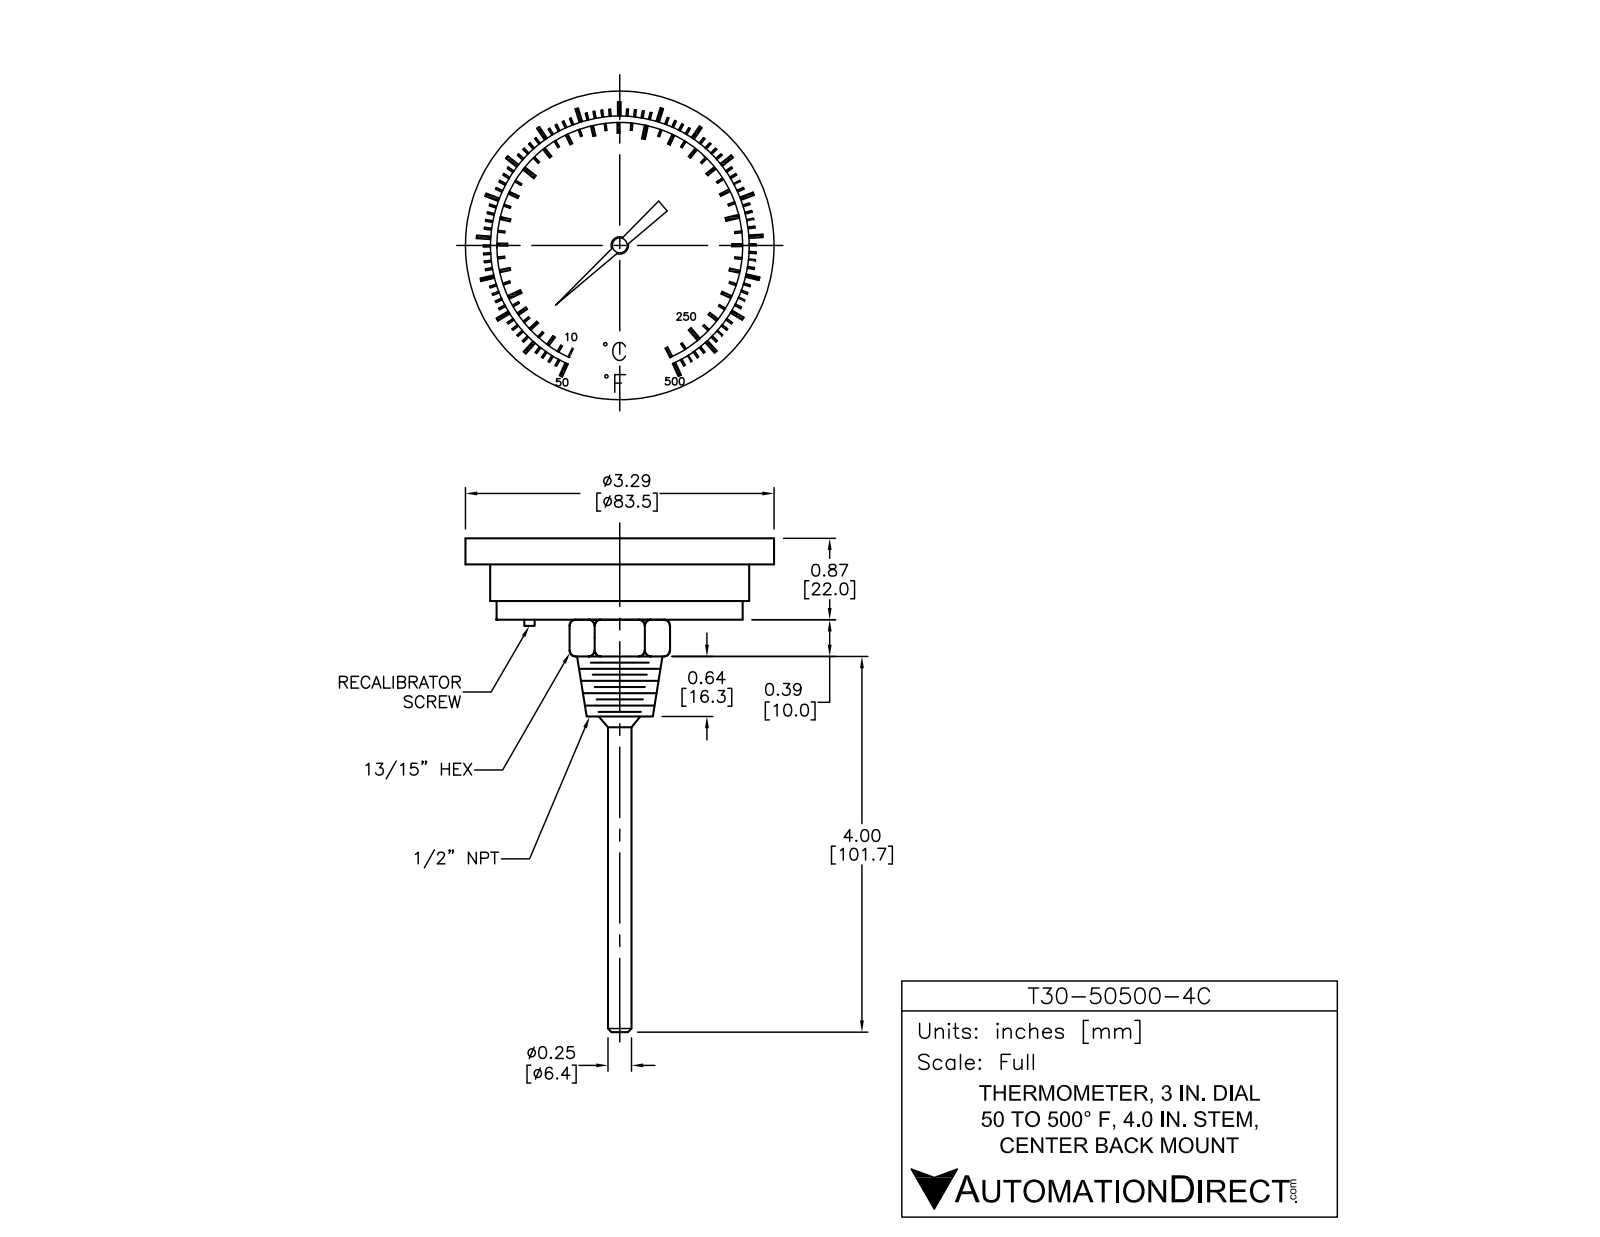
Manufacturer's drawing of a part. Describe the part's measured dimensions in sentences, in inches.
The part is named "T30-50500-4C". Its 3-D file was written by "SolidWorks 2021 (AUTOMOTIVE_DESIGN)". It is 57 solids with 934 faces: 720 planar, 124 cylindrical and 90 other. Overall it measures 5.26 by 3.29 by 3.29 inches. Its volume is 3.15 cubic inches and its surface area 34.08 square inches. Round holes: 1 of diameter 0.067, 1 of diameter 2.69. Round bosses or shafts: 1 of diameter 3.29, 1 of diameter 2.76, 1 of diameter 2.62, 1 of diameter 0.846, 1 of diameter 0.258. Partial cylindrical surfaces (rounded edges, fillets, slot ends): 1 of radius 0.04, 1 of radius 0.859, 1 of radius 0.969. The main face-to-face distances are 0.222, 0.078, 0.3, 0.87, 0.648, 0.57, 0.29, 0.59, 0.368, 0.28.
